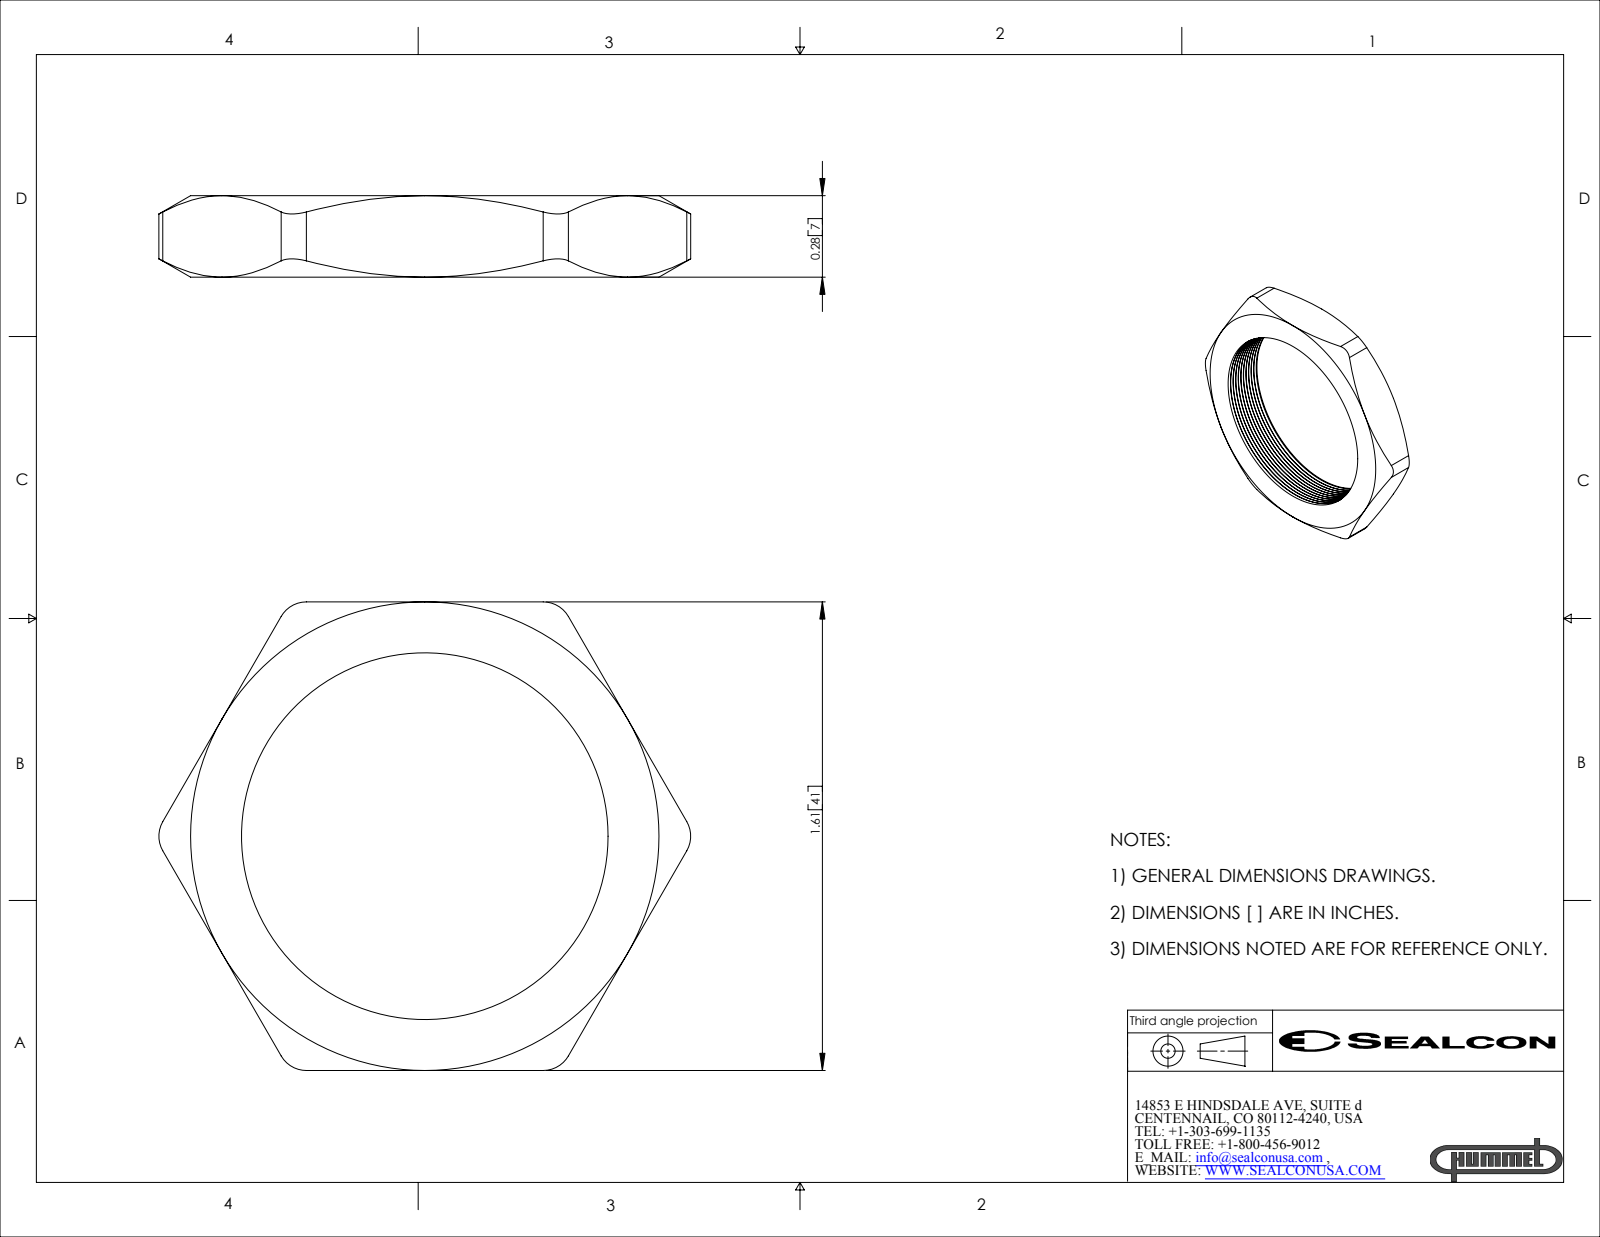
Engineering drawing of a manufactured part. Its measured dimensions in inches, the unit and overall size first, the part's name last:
Units: inches
Overall size (bounding box): 1.828 × 1.61 × 0.28
Round holes (diameter × count): ⌀1.26 ×1
Partial cylindrical surfaces — rounded edges, fillets, slot ends (radius × count): R0.1 ×6
Main face-to-face distances: 0.28, 1.61
Volume: 0.26 in³ · Surface area: 5.48 in²
Bodies: 1 solid, 95 faces (8 planar, 29 cylindrical, 58 other)
Part name (STEP PRODUCT): NM-32-GY
STEP written by: SolidWorks 2007 (CONFIG_CONTROL_DESIGN)
